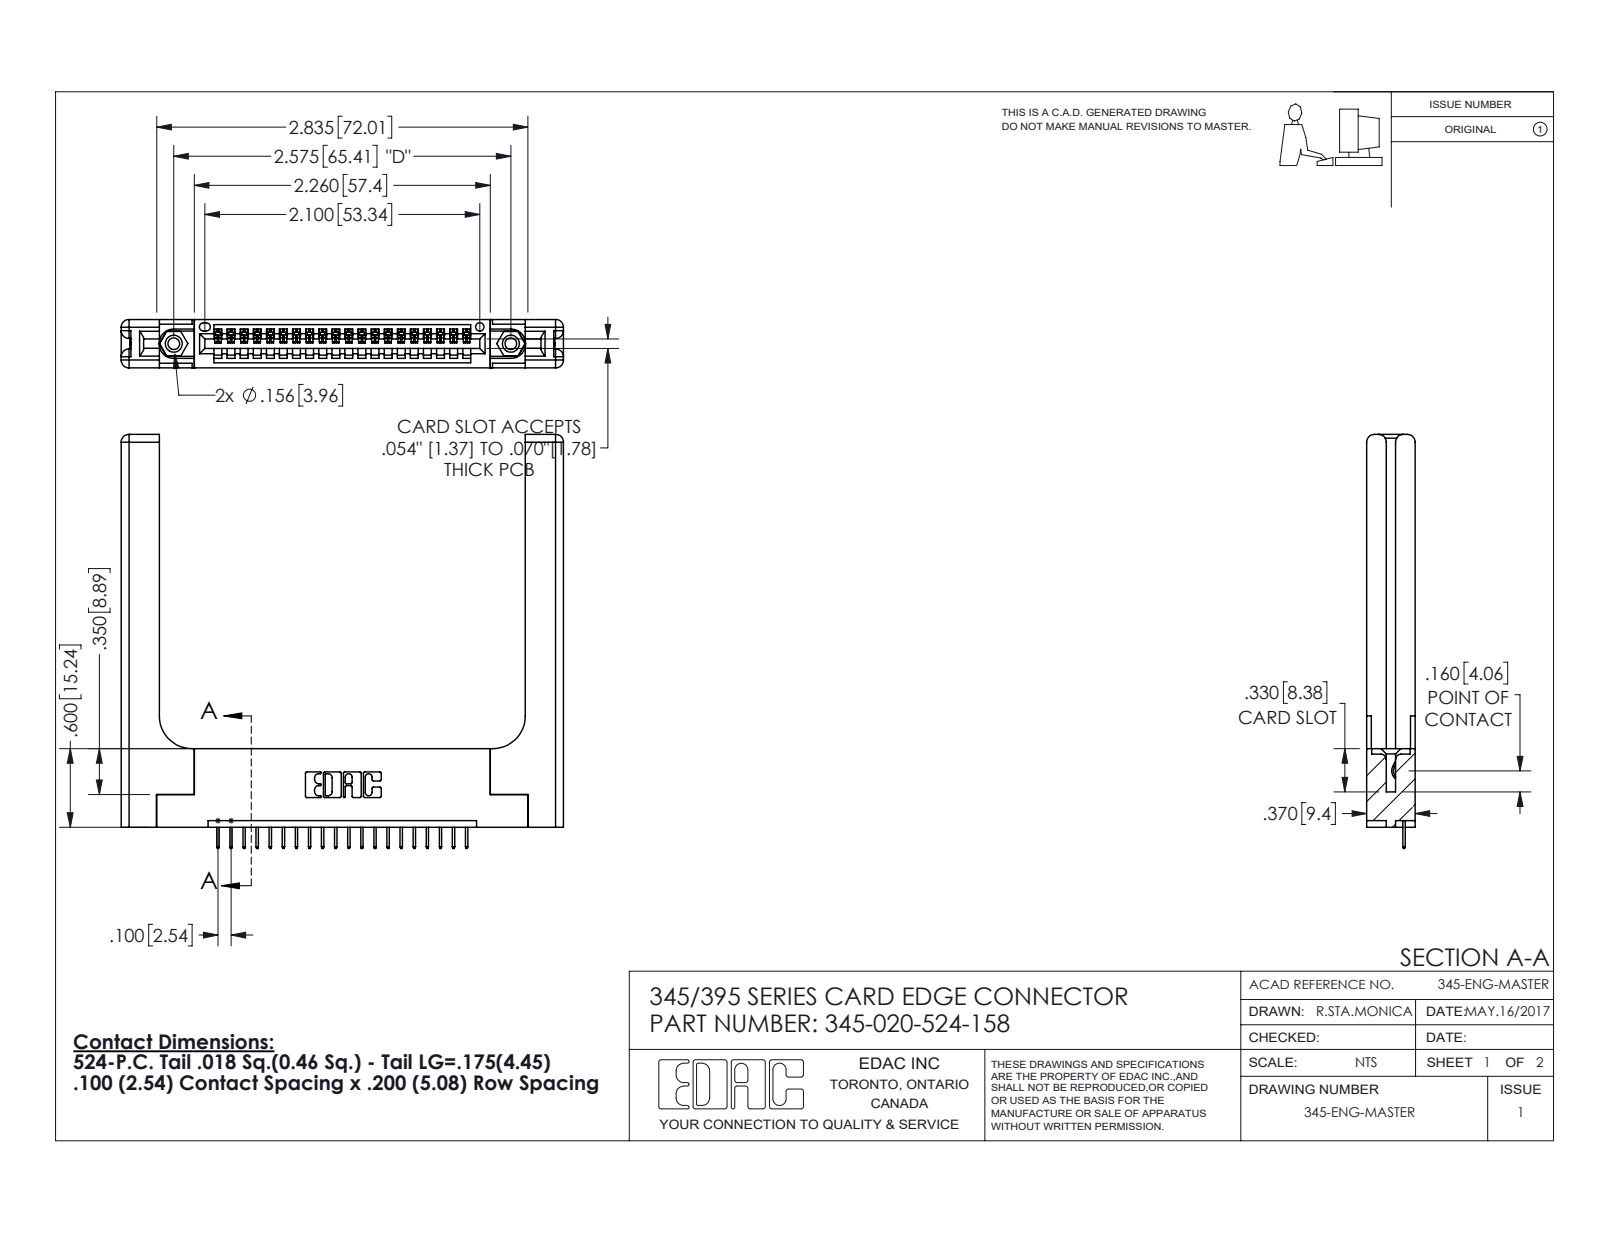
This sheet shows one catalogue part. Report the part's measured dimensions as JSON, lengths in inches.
{"part_name": "345-220-058_345-220-058; 345-292-001_345-293-124; 345-250-001_345-250-001-102; 345 Part_Flush Mounting Lugs - 0.156 Dia-TH (+1 more)", "step_written_by": "SolidWorks 2016 (CONFIG_CONTROL_DESIGN)", "units": "inches", "bodies": {"solids": 25, "faces": 1622, "planar": 1148, "cylindrical": 414, "other": 60}, "overall_size": [3.379, 3.162, 0.37], "volume_in3": 1.001, "surface_area_in2": 23.63, "round_holes": [[0.089, 2], [0.125, 2], [0.156, 2], [0.064, 1]], "round_bosses_or_shafts": [[0.155, 2]], "partial_cylinders_radius": [[0.006, 40], [0.01, 22], [0.06, 16], [0.007, 6], [0.031, 6], [0.026, 3], [0.03, 2], [0.031, 2]], "face_to_face_distances": [0.37, 0.072, 0.298, 0.148, 0.15, 0.077, 0.2, 0.22, 0.098, 0.272], "hole_center_spacings": [0.27, 2.341, 2.575]}
